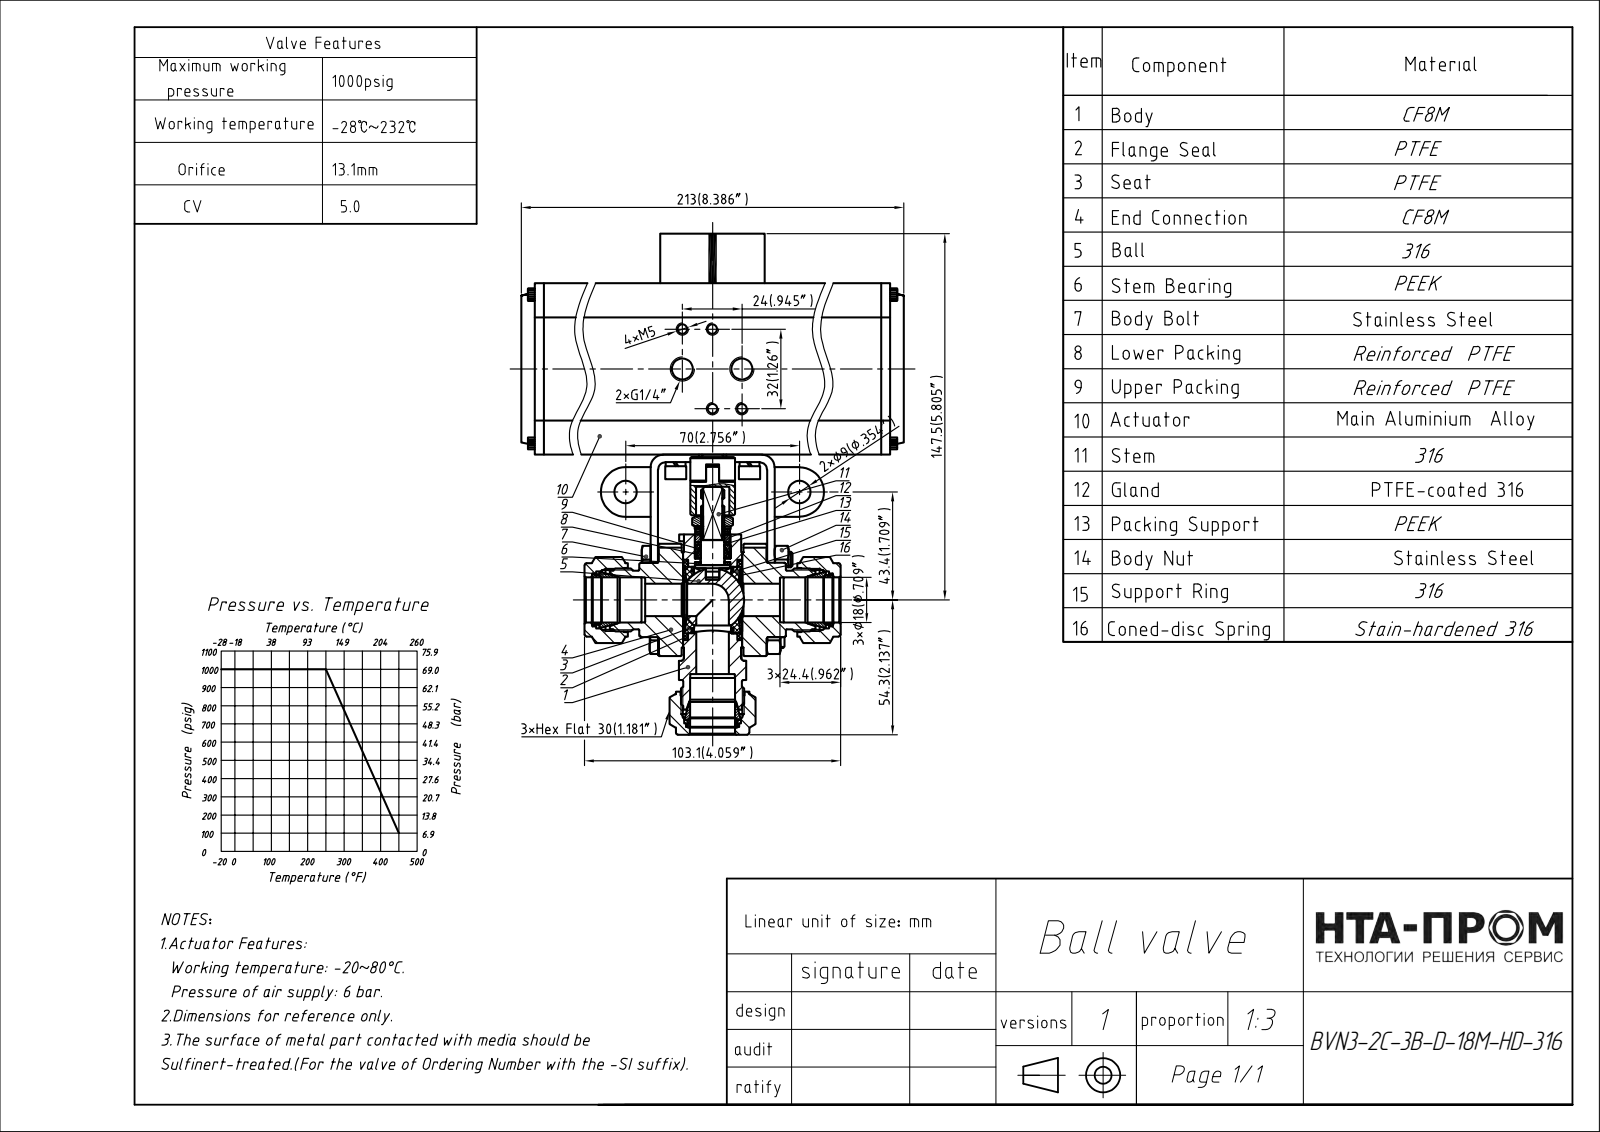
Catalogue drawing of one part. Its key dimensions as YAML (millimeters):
part_name: "BVN3-2C-3B-D-18M-HD-316; 003; 002; 001"
step_written_by: "FreeCAD (AUTOMOTIVE_DESIGN)"
units: millimeters
bodies: {solids: 13, faces: 1407, planar: 511, cylindrical: 496, other: 400}
overall_size: [210, 203.18, 100.2]
volume: 1238000
surface_area: 152542
round_holes:
  - {diameter: 6, count: 8}
  - {diameter: 8, count: 5}
  - {diameter: 4.98, count: 4}
  - {diameter: 6.8, count: 4}
  - {diameter: 5, count: 2}
  - {diameter: 6.76, count: 2}
  - {diameter: 11, count: 2}
  - {diameter: 20, count: 2}
  - {diameter: 6.7, count: 1}
  - {diameter: 9.36, count: 1}
  - {diameter: 13.1, count: 1}
  - {diameter: 18, count: 1}
round_bosses_or_shafts:
  - {diameter: 9.24, count: 4}
  - {diameter: 6, count: 4}
  - {diameter: 29.6, count: 2}
  - {diameter: 25.4, count: 2}
  - {diameter: 23.63, count: 2}
  - {diameter: 8, count: 2}
  - {diameter: 68, count: 1}
  - {diameter: 30, count: 1}
partial_cylinders:
  - {radius: 0.2, count: 16}
  - {radius: 0.5, count: 16}
  - {radius: 1.6, count: 14}
  - {radius: 0.8, count: 8}
  - {radius: 6, count: 6}
  - {radius: 2.36, count: 4}
  - {radius: 5.64, count: 4}
  - {radius: 6.5, count: 4}
face_to_face_distances: [4, 76.8, 76, 67.2, 8.8, 80.8, 2.5, 78.3, 74.3, 83.68]
hole_center_spacings: [23.52, 27.07, 28.81, 32.39, 32.43, 42.72, 43.01, 45.96]
